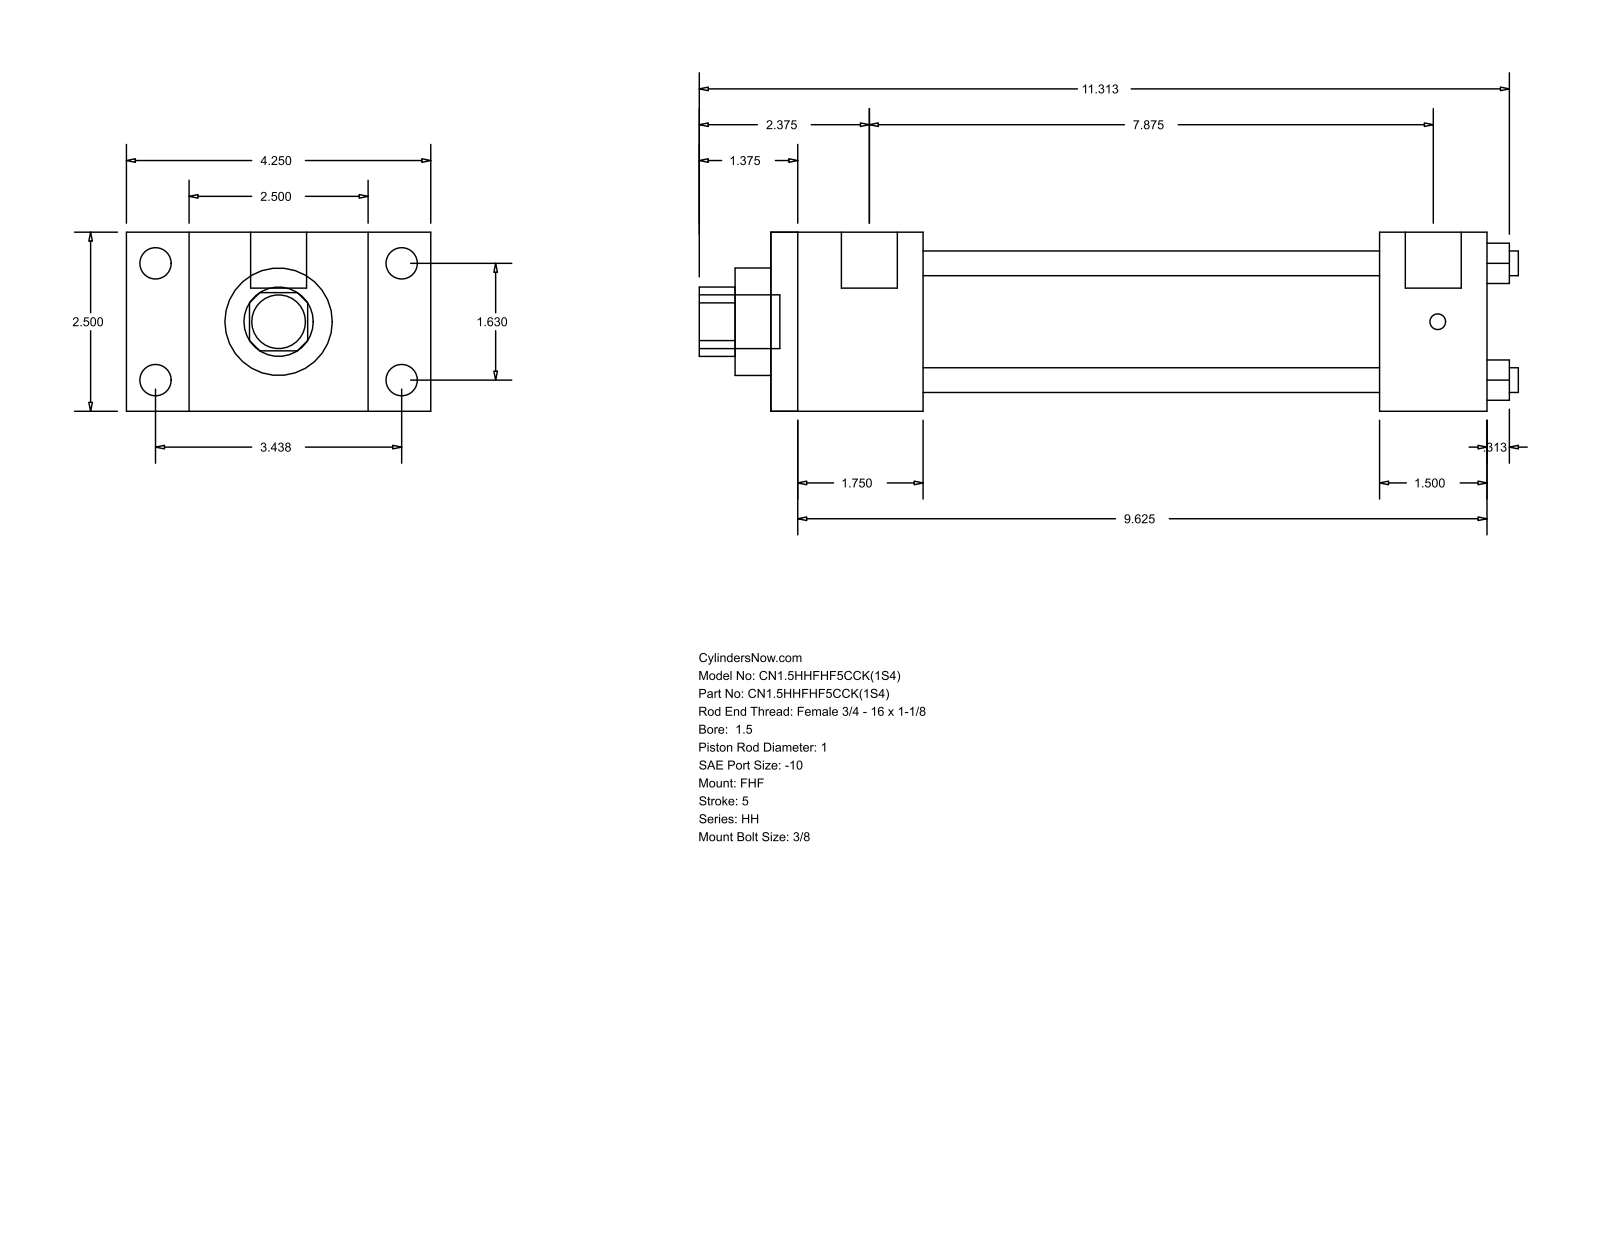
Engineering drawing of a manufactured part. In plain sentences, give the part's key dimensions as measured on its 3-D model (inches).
The part is named "HH_FHF__0150_1". Its 3-D file was written by "GSSL Pune (CONFIG_CONTROL_DESIGN)". It is 0 solids with 88 faces: 60 planar, 28 cylindrical and 0 other. Overall it measures 11.437 by 4.25 by 2.5 inches. Round holes: 4 of diameter 0.345, 1 of diameter 1, 1 of diameter 1.5, 1 of diameter 1.75. Round bosses or shafts: 4 of diameter 0.438, 4 of diameter 0.219, 2 of diameter 0.781, 1 of diameter 0.75. Partial cylindrical surfaces (rounded edges, fillets, slot ends): 1 of radius 0.484. The main face-to-face distances are 2.5, 0.875, 3.375, 2.125, 4.25, 10, 7.875, 8.5, 6.375, 1.5. The hole center spacings are 1.152, 1.63, 2.305.
